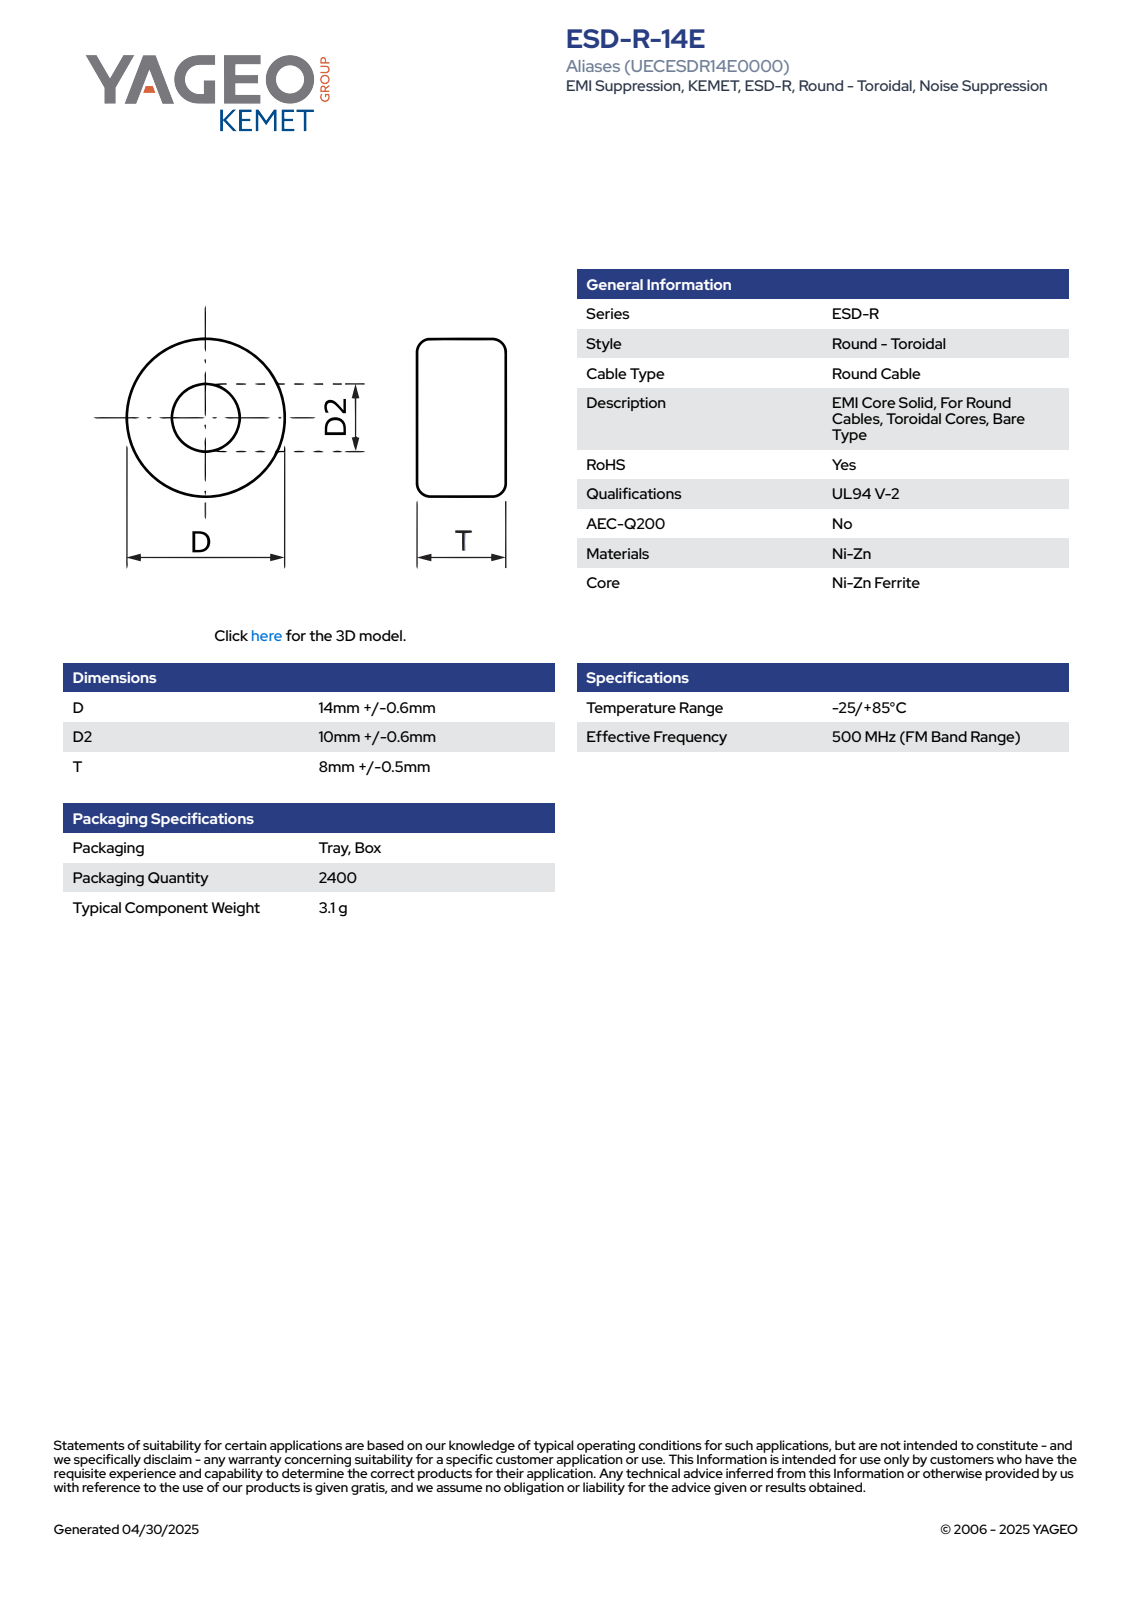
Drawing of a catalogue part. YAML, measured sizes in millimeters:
part_name: "EC_KBC_D14.6D210T8.5"
step_written_by: "SolidWorks 2021 (AUTOMOTIVE_DESIGN)"
units: millimeters
bodies: {solids: 1, faces: 66, planar: 24, cylindrical: 7, other: 35}
overall_size: [14.61, 14.6, 8.5]
volume: 751
surface_area: 819
round_holes:
  - {diameter: 10, count: 1}
round_bosses_or_shafts:
  - {diameter: 14.6, count: 1}
partial_cylinders:
  - {radius: 7.31, count: 1}
face_to_face_distances: [8.5, 3.4, 5.1, 1.7, 0.32, 3.72, 4.78, 1.38, 1.06, 4.46]
